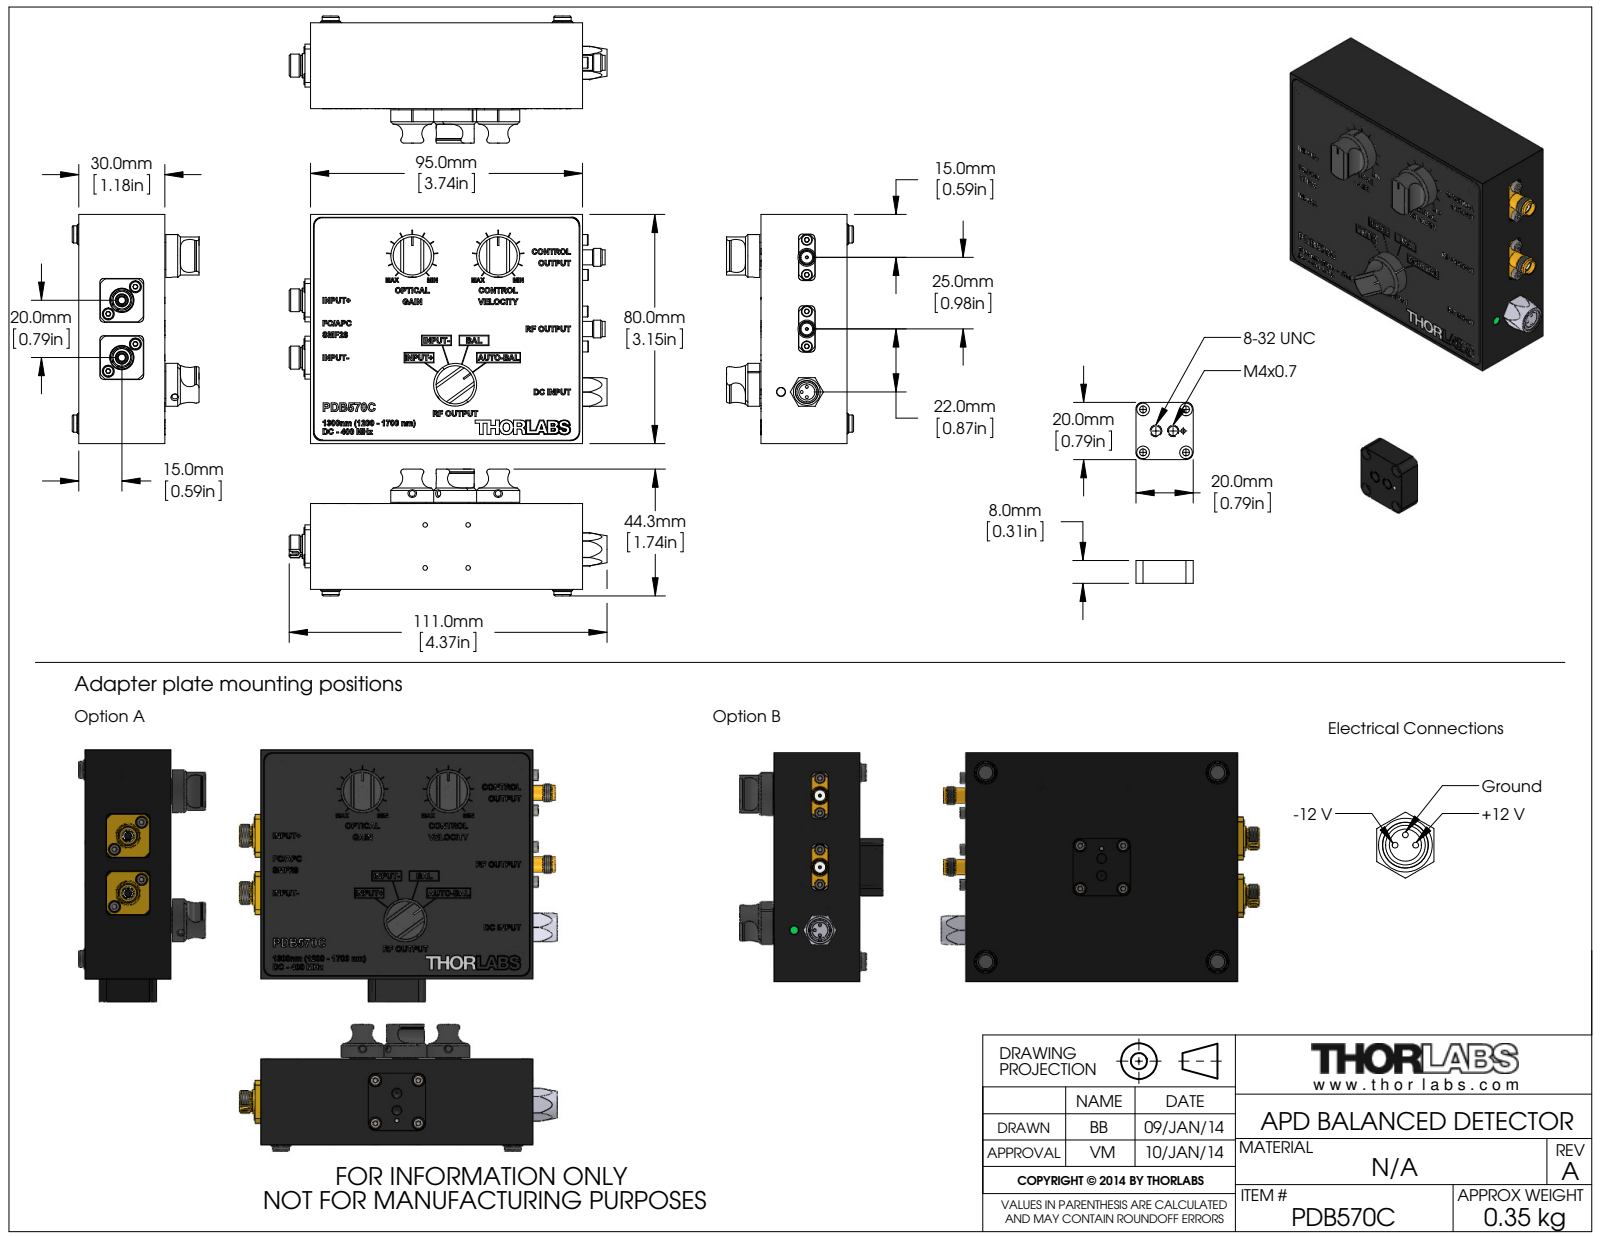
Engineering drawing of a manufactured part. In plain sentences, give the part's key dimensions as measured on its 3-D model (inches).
The part is named "MTN003677". Its 3-D file was written by "SolidWorks 2013 (AUTOMOTIVE_DESIGN)". It is 0 solids with 826 faces: 453 planar, 228 cylindrical and 145 other. Overall it measures 4.37 by 3.15 by 1.969 inches. Round holes: 7 of diameter 0.315, 4 of diameter 0.063, 4 of diameter 0.173, 3 of diameter 0.039, 3 of diameter 0.081, 2 of diameter 0.161, 2 of diameter 0.172, 2 of diameter 0.185, 2 of diameter 0.276, 2 of diameter 0.335, 1 of diameter 0.122, 1 of diameter 0.13. Round bosses or shafts: 8 of diameter 0.15, 4 of diameter 0.236, 4 of diameter 0.165, 3 of diameter 0.591, 3 of diameter 0.524, 2 of diameter 0.245, 2 of diameter 0.24, 2 of diameter 0.209. Partial cylindrical surfaces (rounded edges, fillets, slot ends): 16 of radius 0.059, 12 of radius 0.039, 8 of radius 0.118, 6 of radius 0.13, 4 of radius 0.098, 3 of radius 0.295, 2 of radius 0.04, 2 of radius 0.315. The main face-to-face distances are 1.181, 3.15, 3.74, 1.969, 0.295, 1.169, 0.787, 2.264, 0.315, 1.484. The hole center spacings are 0.591, 0.344, 0.508, 0.835, 1.642, 1.984, 2.057, 2.133.
